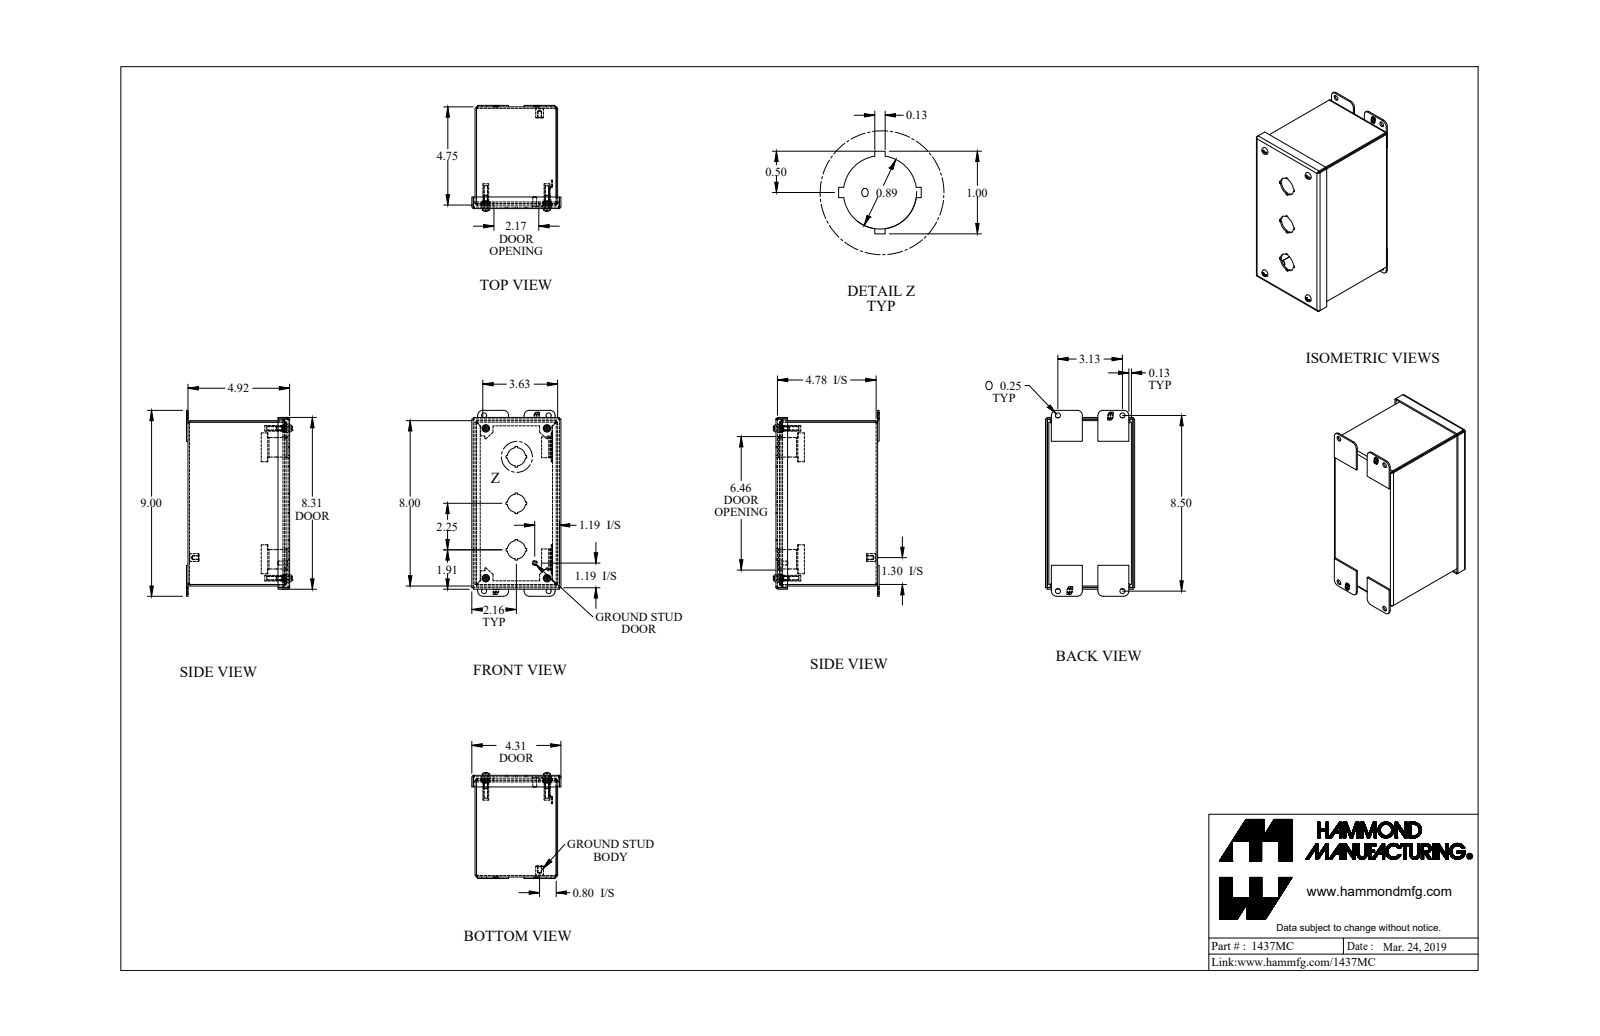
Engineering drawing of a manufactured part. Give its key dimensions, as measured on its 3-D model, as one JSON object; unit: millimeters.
{"part_name": "1437MC_Default", "step_written_by": "SolidWorks 2019 (CONFIG_CONTROL_DESIGN)", "units": "millimeters", "bodies": {"solids": 23, "faces": 763, "planar": 535, "cylindrical": 172, "other": 56}, "overall_size": [228.6, 130.1, 109.5], "volume_mm3": 280900, "surface_area_mm2": 295500, "round_holes": [[6.4, 8], [4, 4], [10.3, 4], [22.5, 3], [4, 1]], "round_bosses_or_shafts": [[9.9, 4], [7, 4], [4.8, 4], [3.8, 4], [9.5, 1], [6.4, 1], [4.8, 1]], "partial_cylinders_radius": [[0.9, 12], [2.7, 12], [6.4, 8], [0.7, 4], [2.2, 4], [4.1, 4], [4.3, 4], [3.2, 2]], "face_to_face_distances": [1.8, 99.8, 123.2, 125, 101.6, 97.9, 201.4, 121.4, 4, 203.2], "hole_center_spacings": [16, 99.5, 153.9, 184.2, 200.1, 214.5, 51.3, 78.9]}
